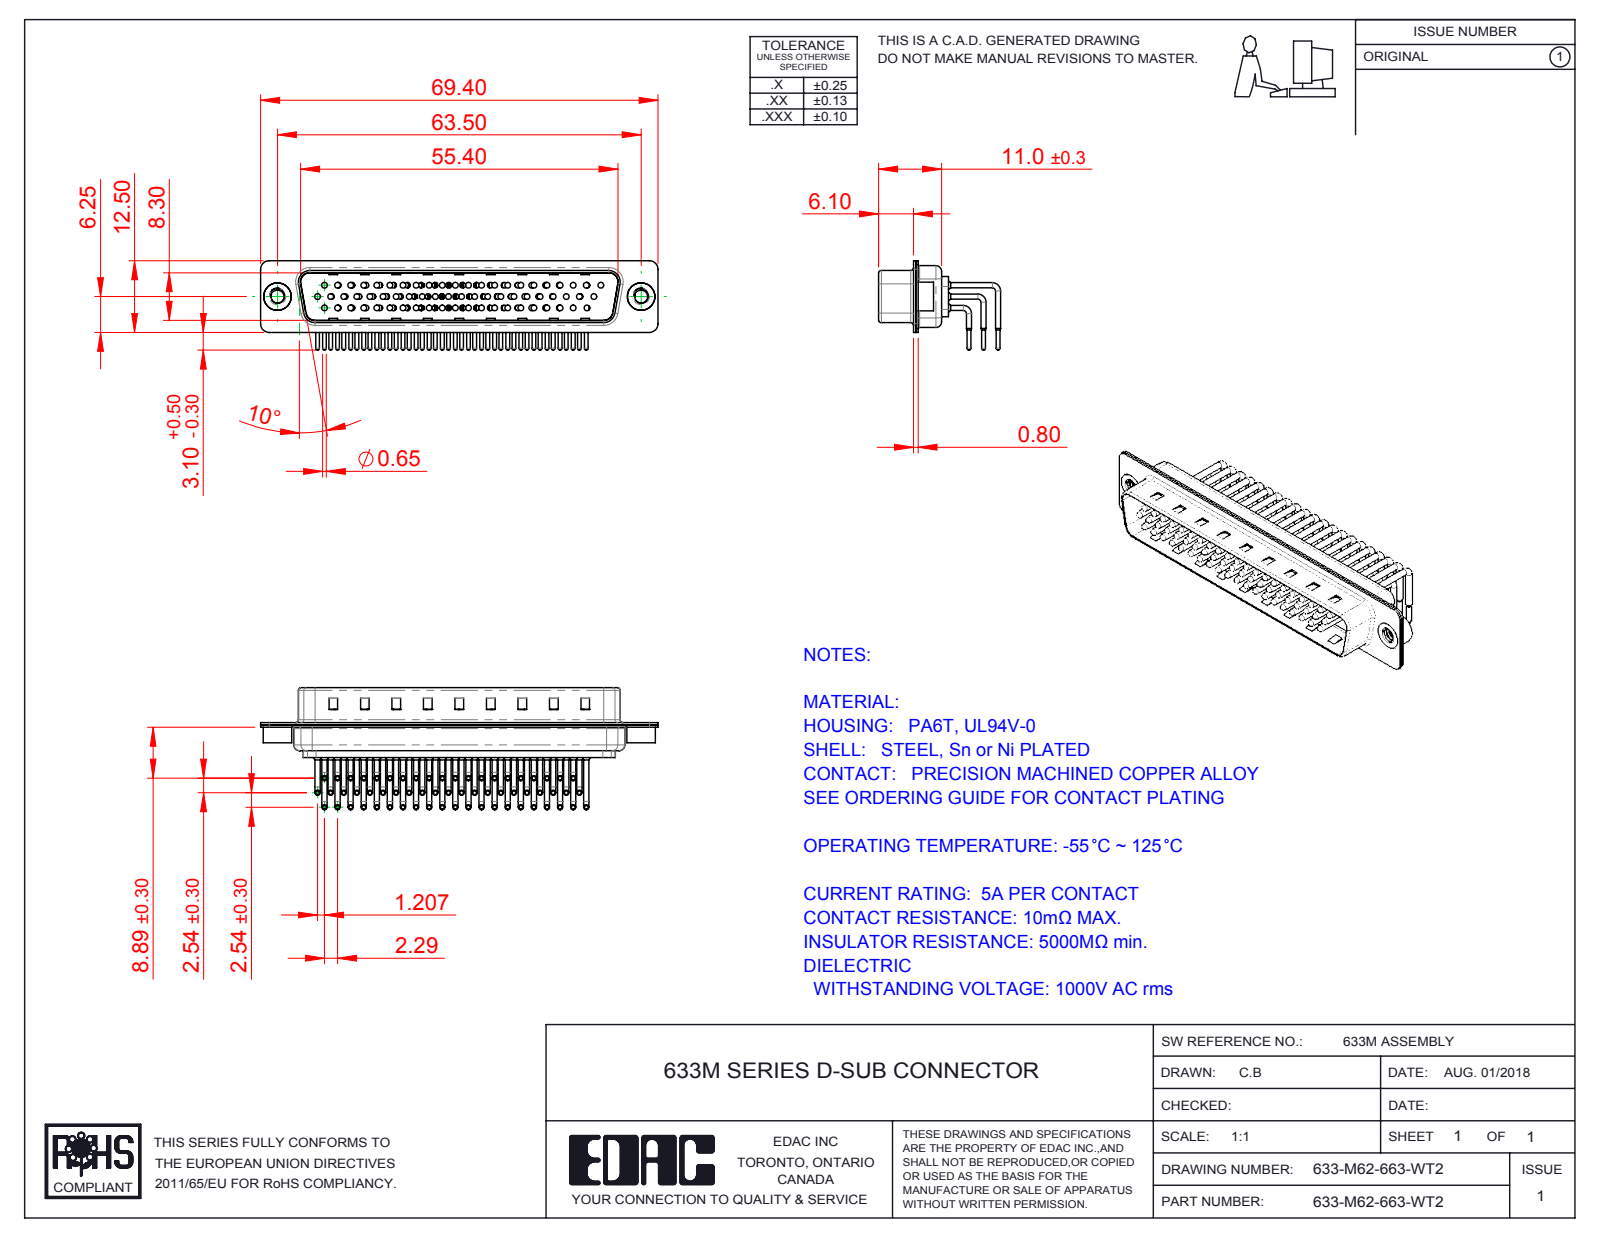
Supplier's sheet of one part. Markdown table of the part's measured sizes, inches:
| quantity | value |
| --- | --- |
| part name | 633M Housing_62 Contacts; 633M Contact Row 2; 633M Contact Row 3; 633M Contact Row 1 (+4 more) |
| STEP written by | SolidWorks 2016 (CONFIG_CONTROL_DESIGN) |
| units | inches |
| bodies | 67 solids, 7232 faces (4171 planar, 2373 cylindrical, 688 other) |
| overall size | 2.732 × 0.839 × 0.614 |
| volume | 0.265 in³ |
| surface area | 21.15 in² |
| round holes (diameter × count) | 0.039 × 62, 0.067 × 62, 0.079 × 62, 0.089 × 2, 0.157 × 2, 0.189 × 2 |
| round bosses / shafts (diameter × count) | 0.035 × 124, 0.059 × 62, 0.026 × 62, 0.039 × 56, 0.197 × 2, 0.193 × 2 |
| partial cylindrical surfaces (radius × count) | 0.04 × 62, 0.059 × 16, 0.079 × 12, 0.02 × 8, 0.063 × 8, 0.01 × 4, 0.024 × 4, 0.026 × 4 |
| main face-to-face distances | 0.016, 0.033, 0.376, 0.343, 0.059, 0.075, 0.049, 0.409, 0.014, 0.018 |
| hole center spacings | 0.285, 0.091, 0.095, 0.163, 0.38, 0.19, 0.57, 0.435 |
